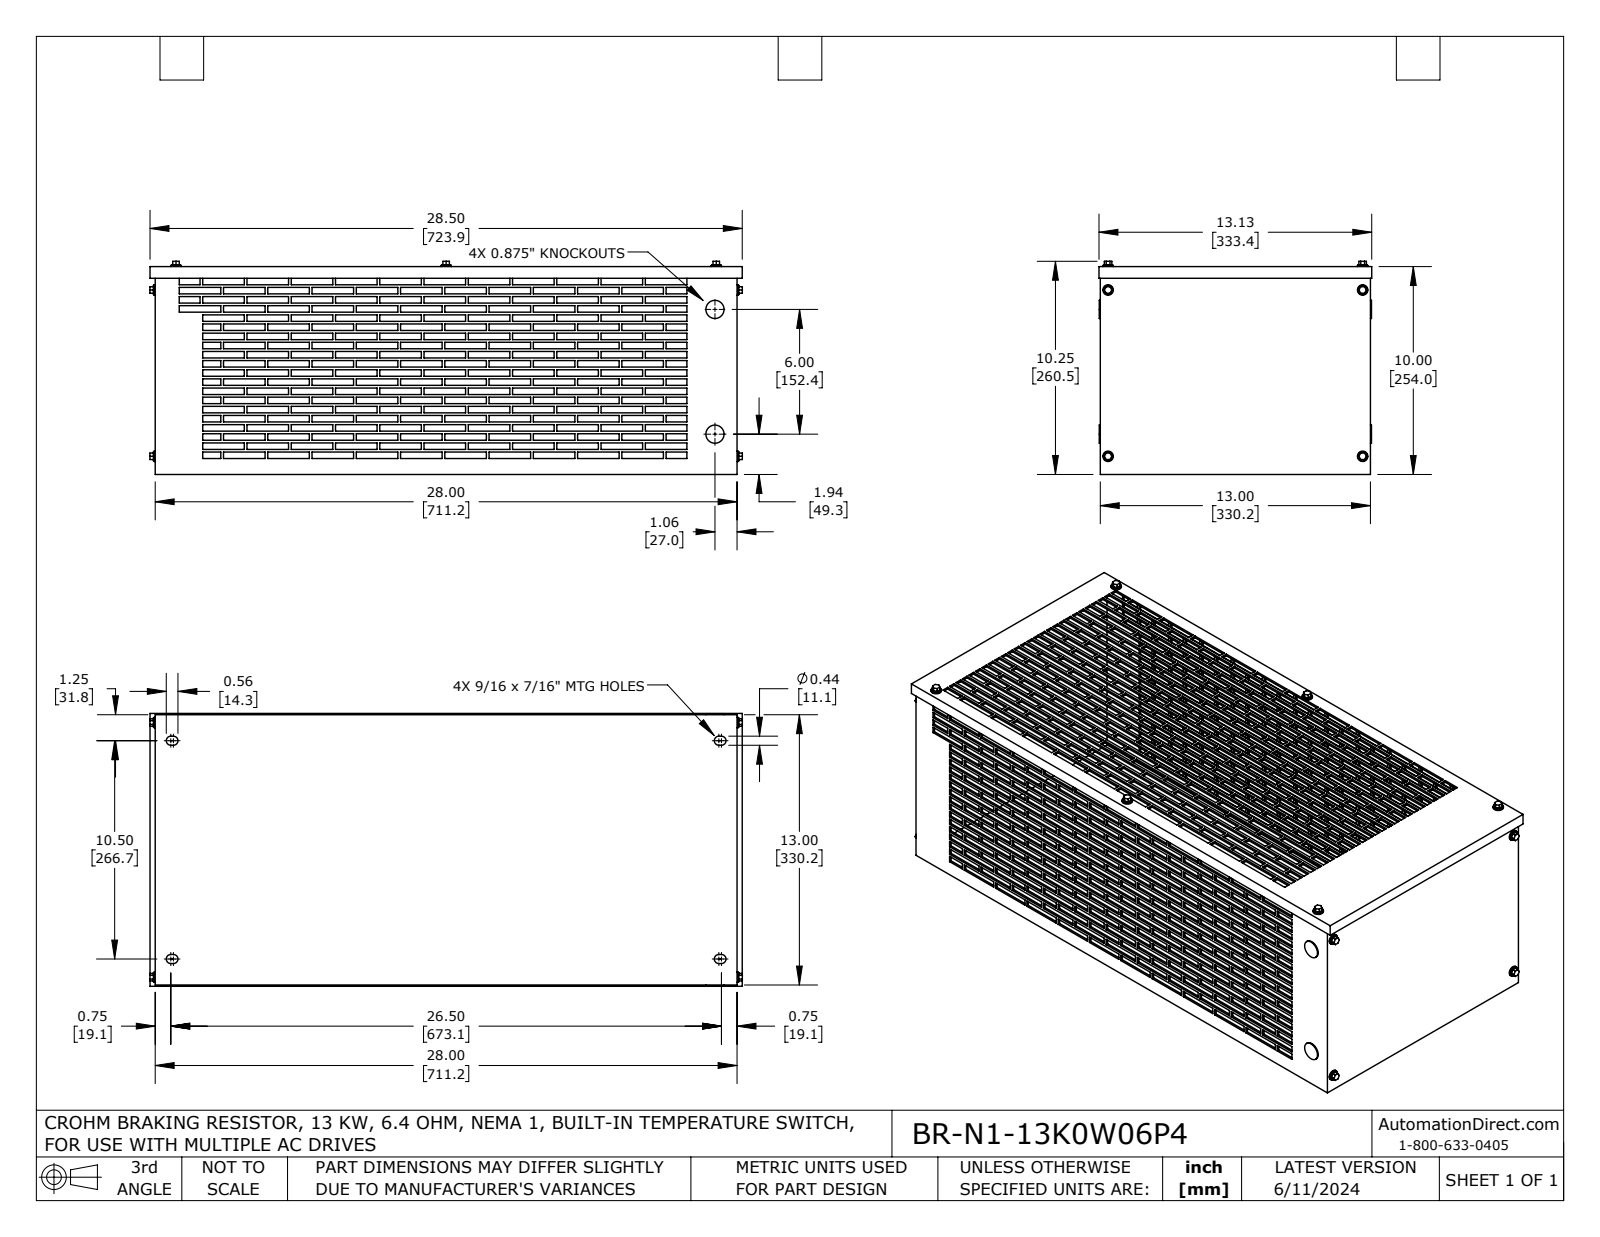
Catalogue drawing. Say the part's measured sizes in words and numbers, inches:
The part is named "BR-N1-13K0W06P4". Its 3-D file was written by "SolidWorks 2021 (AUTOMOTIVE_DESIGN)". It is 33 solids with 3380 faces: 3272 planar, 108 cylindrical and 0 other. Overall it measures 28.509 by 13.125 by 10.254 inches. Its volume is 108.9 cubic inches and its surface area 2 534 square inches. Round holes: 10 of diameter 0.25, 2 of diameter 0.75. Round bosses or shafts: 10 of diameter 0.5, 10 of diameter 0.437, 2 of diameter 0.875. Partial cylindrical surfaces (rounded edges, fillets, slot ends): 8 of radius 0.219. The main face-to-face distances are 0.1, 9.9, 12.9, 27.9, 10, 9.8, 13, 28, 12.8, 27.8. The hole center spacings are 12.25, 13, 17.862, 8, 14.631, 26, 28.741, 6.
